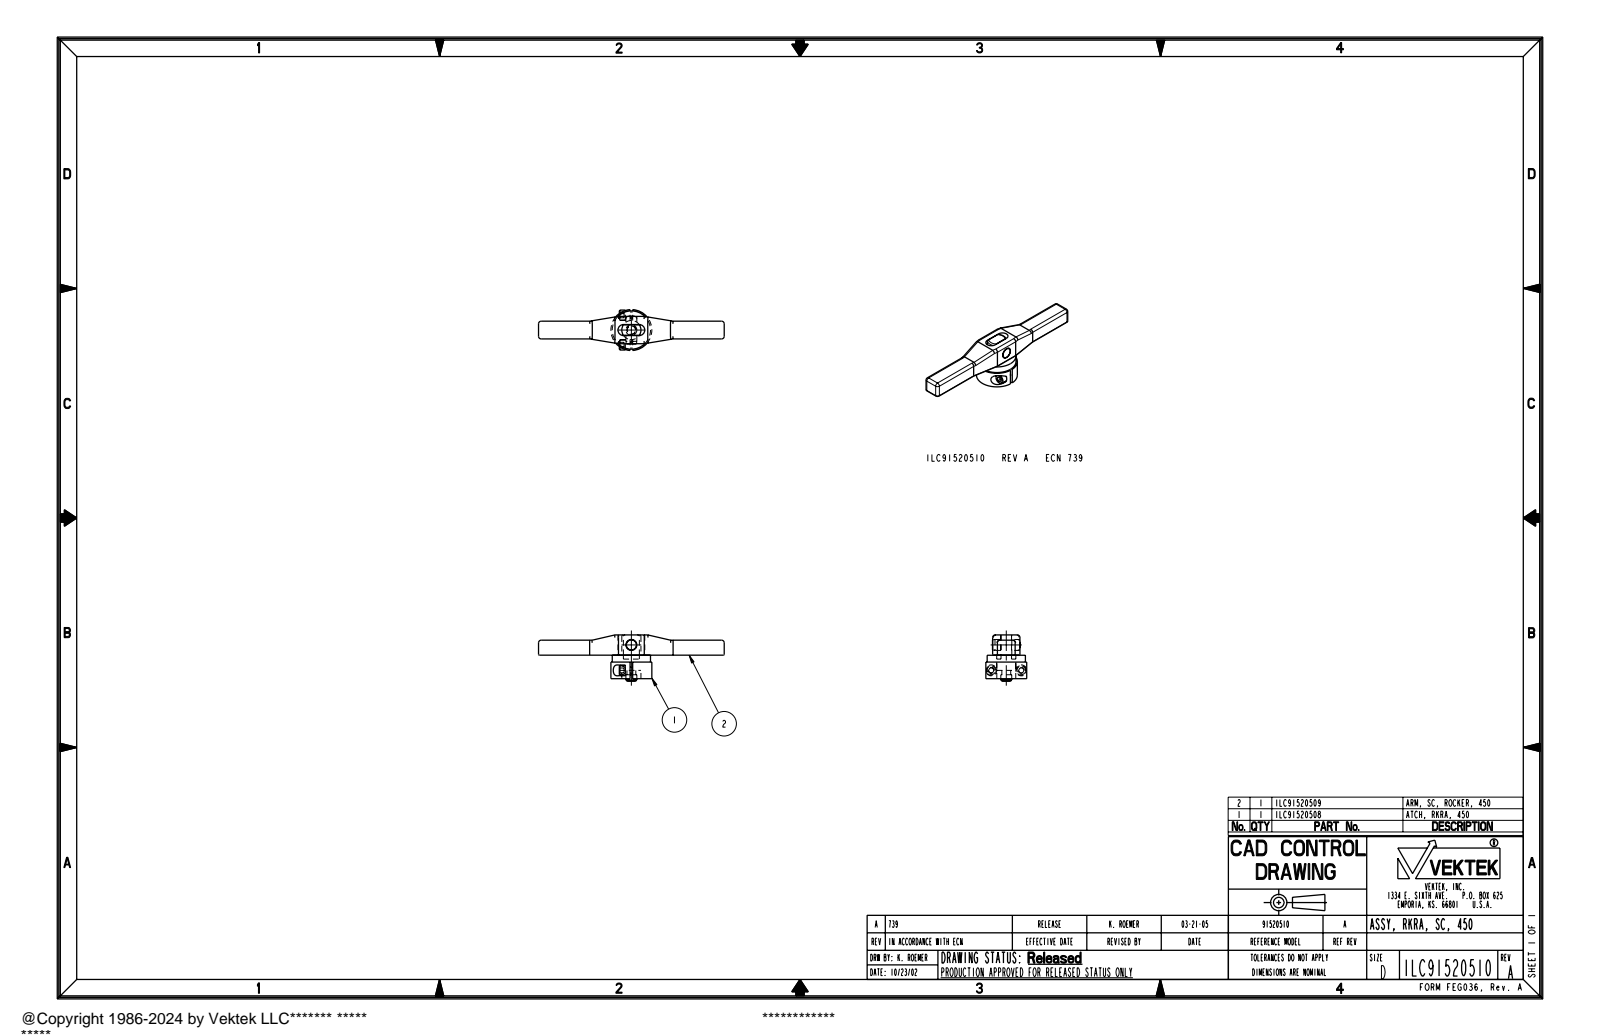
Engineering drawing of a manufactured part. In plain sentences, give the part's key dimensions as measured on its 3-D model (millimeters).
The part is named "ILC91520508; ILC91520509; ILC91520510_ASM". Its 3-D file was written by "PRO/ENGINEER BY PARAMETRIC TECHNOLOGY CORPORATION, 2004290 (AUTOMOTIVE_DESIGN_CC2)". It is 2 solids with 153 faces: 61 planar, 72 cylindrical and 20 other. Overall it measures 108 by 27 by 23.7 millimeters. Its volume is 17 440 cubic millimeters and its surface area 8 277 square millimeters. Round holes: 2 of diameter 6.4, 1 of diameter 6.4, 1 of diameter 11.1. Round bosses or shafts: 2 of diameter 5.7, 2 of diameter 3.5, 1 of diameter 23.8, 1 of diameter 22.2, 1 of diameter 6.4, 1 of diameter 6.4, 1 of diameter 5.2. Partial cylindrical surfaces (rounded edges, fillets, slot ends): 22 of radius 1.5, 10 of radius 0.5, 2 of radius 3.2. The main face-to-face distances are 8.7, 10.3, 13.7, 22.4, 13.6, 8.8, 11, 2.8, 13.1, 4.9. The hole center spacings are 17.5.
